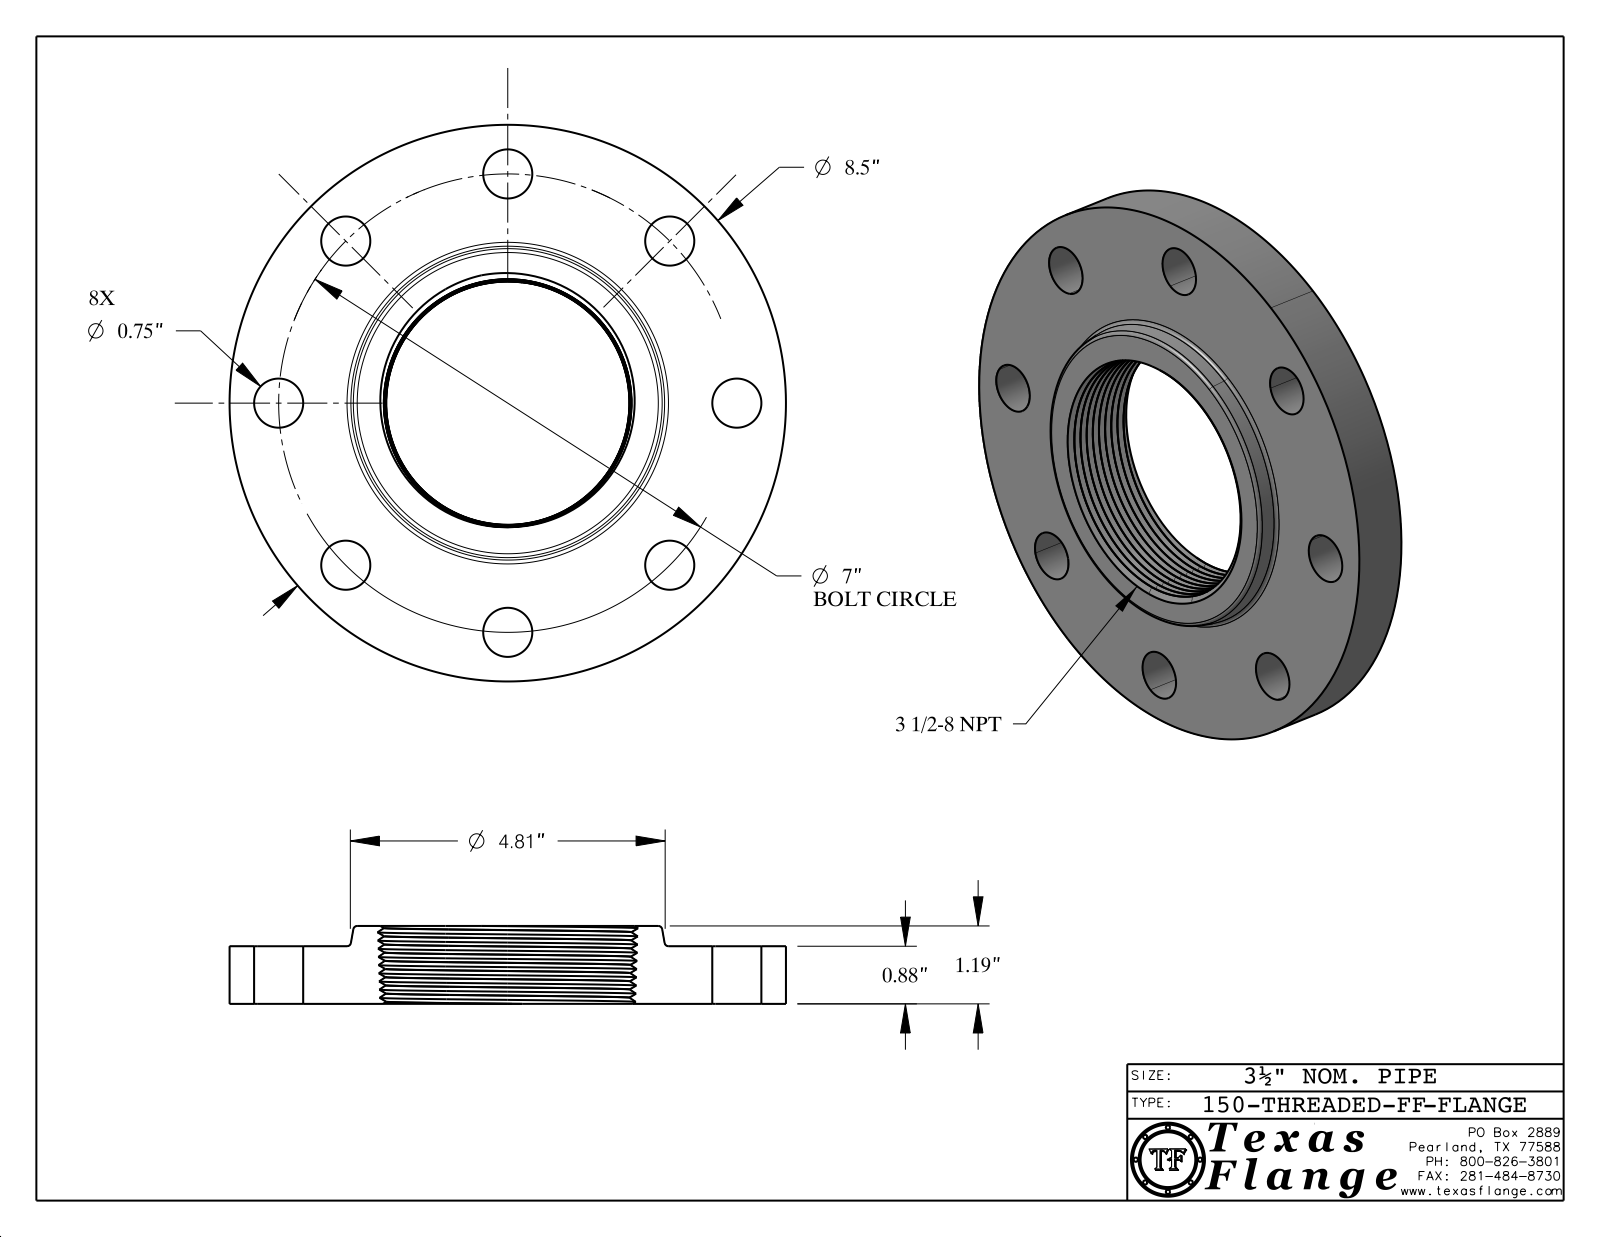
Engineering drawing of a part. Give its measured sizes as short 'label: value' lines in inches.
name: 150-THREADED-FF
written by: CATIA V5 STEP AP214 (AUTOMOTIVE_DESIGN)
unit: in
bodies: 1 solid, 515 faces (368 planar, 38 cylindrical, 109 other)
size: 8.5 × 8.5 × 1.19
volume: 38.49 in³; area: 153.7 in²
holes: 8× ⌀0.75, 1× ⌀0.495
bosses: 8× ⌀0.03, 1× ⌀8.5, 1× ⌀0.39
face distances: 0.88, 1.19, 0.31, 0.865, 0.015, 0.325, 0.148, 0.145, 0.027, 0.122
hole spacings: 2.679, 4.95, 6.467, 1.366, 3.889, 5.82, 6.865, 7
